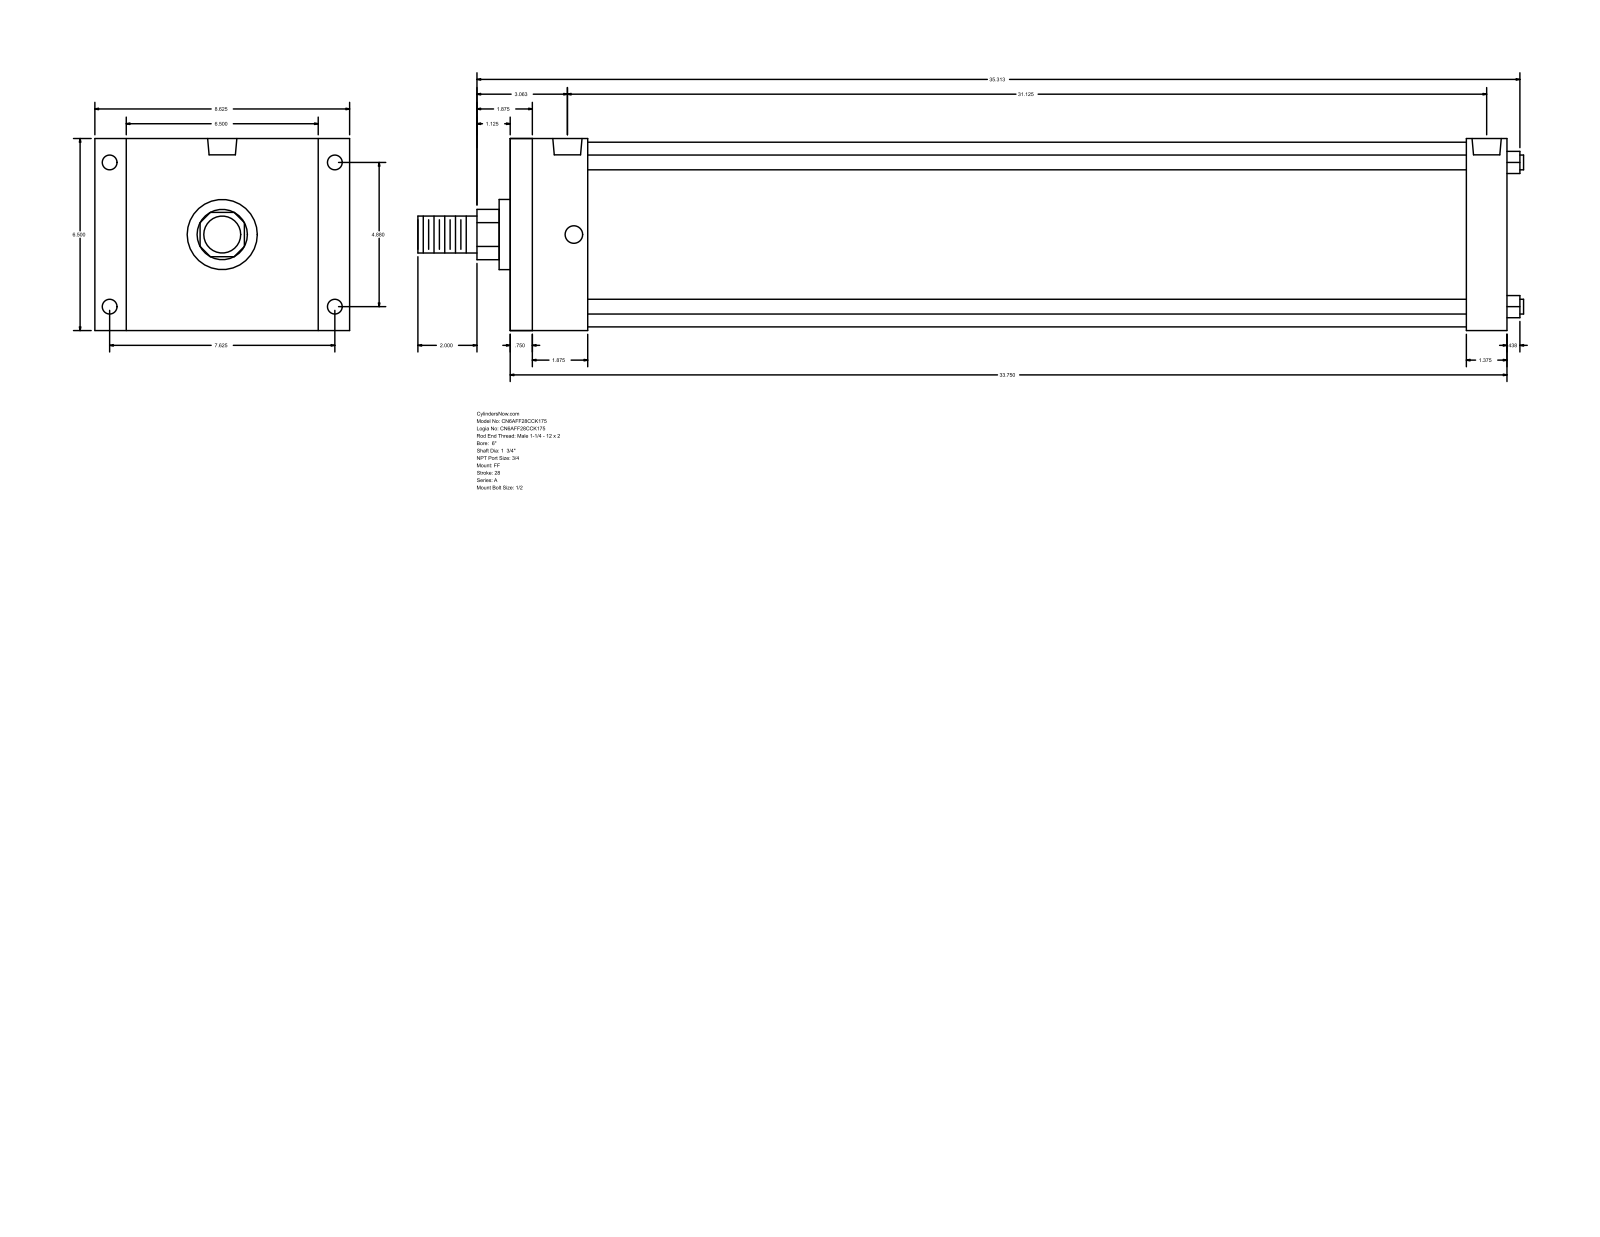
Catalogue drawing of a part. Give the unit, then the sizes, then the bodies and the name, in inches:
Units: inches
Overall size (bounding box): 37.437 × 8.625 × 6.5
Round holes (diameter × count): ⌀0.5 ×4, ⌀0.594 ×4, ⌀0.989 ×2
Round bosses / shafts (diameter × count): ⌀0.5 ×4, ⌀6.25 ×1, ⌀2.375 ×1, ⌀1.75 ×1, ⌀1.25 ×1
Partial cylindrical surfaces — rounded edges, fillets, slot ends (radius × count): R0.852 ×1
Main face-to-face distances: 6.5, 33.75, 0.75, 33, 2.625, 1.875, 31.125, 32.375, 31.625, 29.75
Hole centre spacings: 0.219, 4.88, 7.625, 9.053, 30.687, 30.906, 31.125
Bodies: 0 solids, 92 faces (64 planar, 28 cylindrical, 0 other)
Part name (STEP PRODUCT): A_FF__0600_1.75
STEP written by: GSSL Pune (CONFIG_CONTROL_DESIGN)
